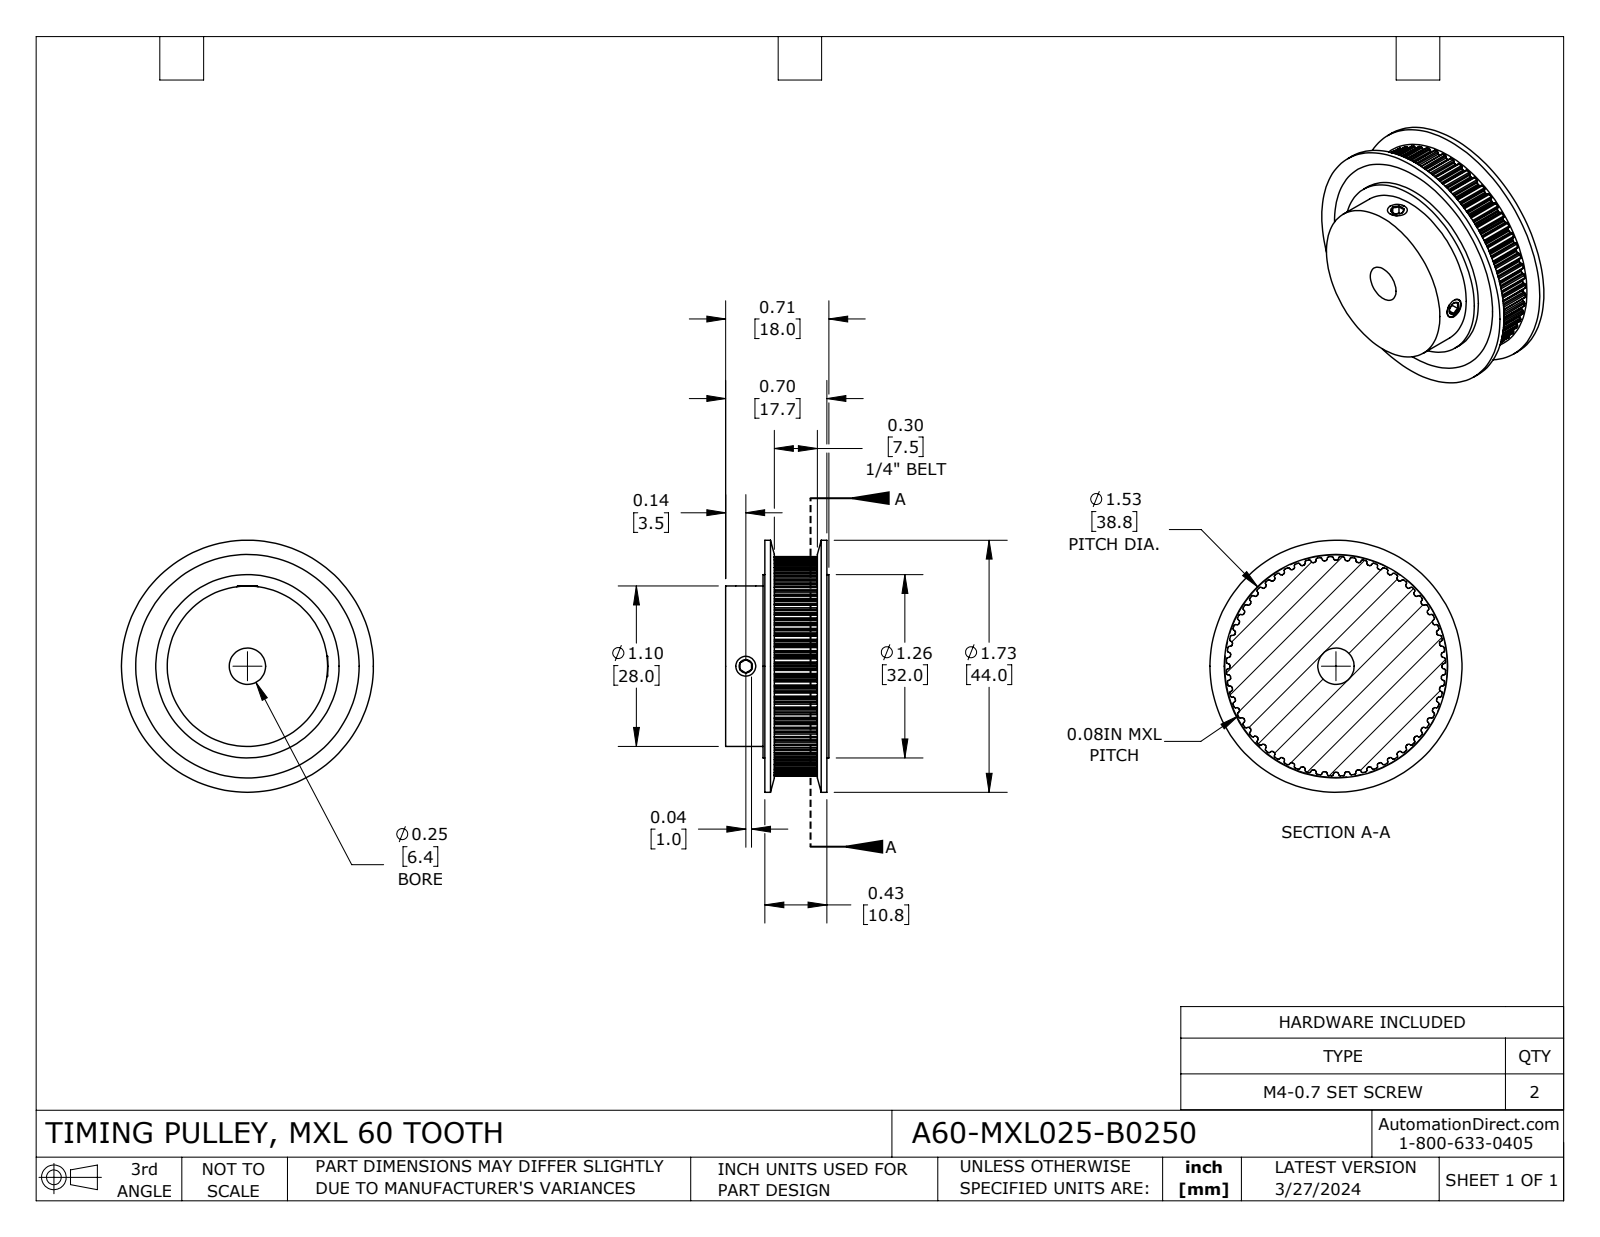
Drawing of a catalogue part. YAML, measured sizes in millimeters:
part_name: "A60-MXL025-B0250"
step_written_by: "SolidWorks 2021 (CONFIG_CONTROL_DESIGN)"
units: millimeters
bodies: {solids: 5, faces: 612, planar: 145, cylindrical: 433, other: 34}
overall_size: [44, 44, 18]
volume: 16336
surface_area: 8429
round_holes:
  - {diameter: 3.3, count: 2}
  - {diameter: 6.35, count: 1}
  - {diameter: 32, count: 1}
round_bosses_or_shafts:
  - {diameter: 4, count: 2}
  - {diameter: 44, count: 1}
  - {diameter: 28, count: 1}
partial_cylinders:
  - {radius: 0.23, count: 120}
  - {radius: 0.3, count: 120}
  - {radius: 18.51, count: 1}
  - {radius: 19.15, count: 1}
face_to_face_distances: [8.5, 1, 9.5, 7.5, 2, 18, 16, 10.5, 17, 11.5]
